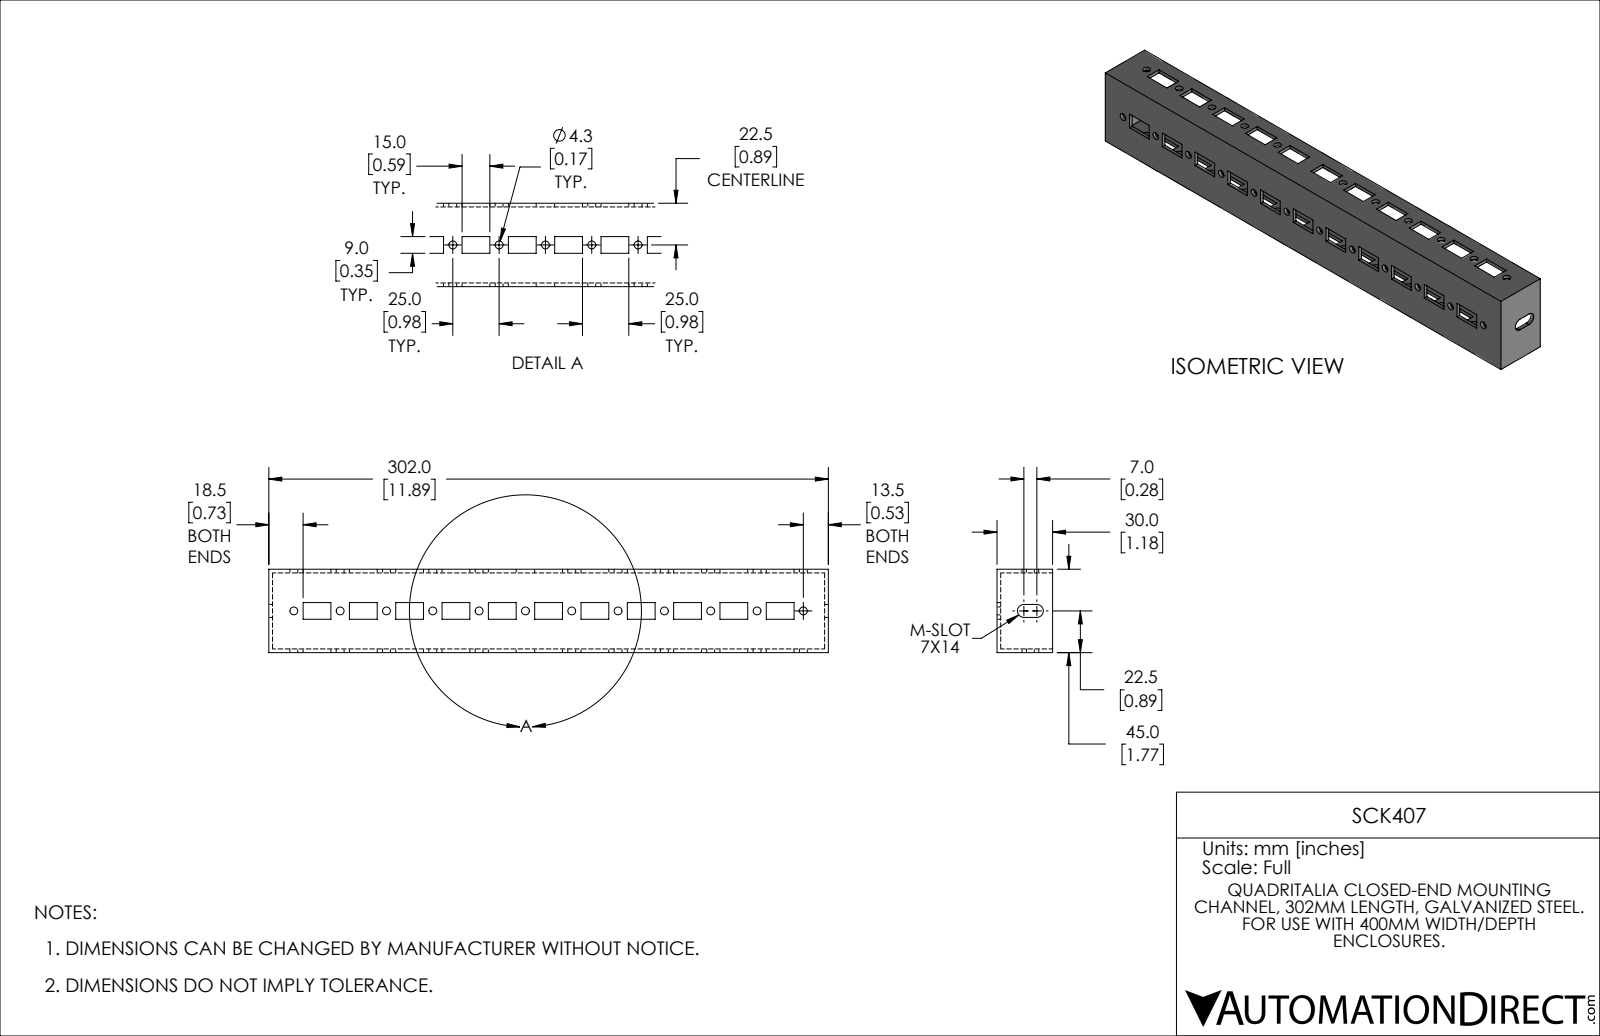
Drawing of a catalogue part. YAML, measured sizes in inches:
part_name: "SCK407"
step_written_by: "SolidWorks 2021 (CONFIG_CONTROL_DESIGN)"
units: inches
bodies: {solids: 1, faces: 185, planar: 147, cylindrical: 38, other: 0}
overall_size: [11.89, 1.772, 1.181]
volume: 3.379
surface_area: 94.52
round_holes:
  - {diameter: 0.167, count: 23}
partial_cylinders:
  - {radius: 0.138, count: 2}
face_to_face_distances: [0.079, 1.693, 1.772, 1.614, 11.811, 0.984, 1.181, 1.102, 11.89, 11.732]
hole_center_spacings: [0.984, 1.969, 2.953, 3.937, 4.921, 5.906, 6.89, 7.874]
